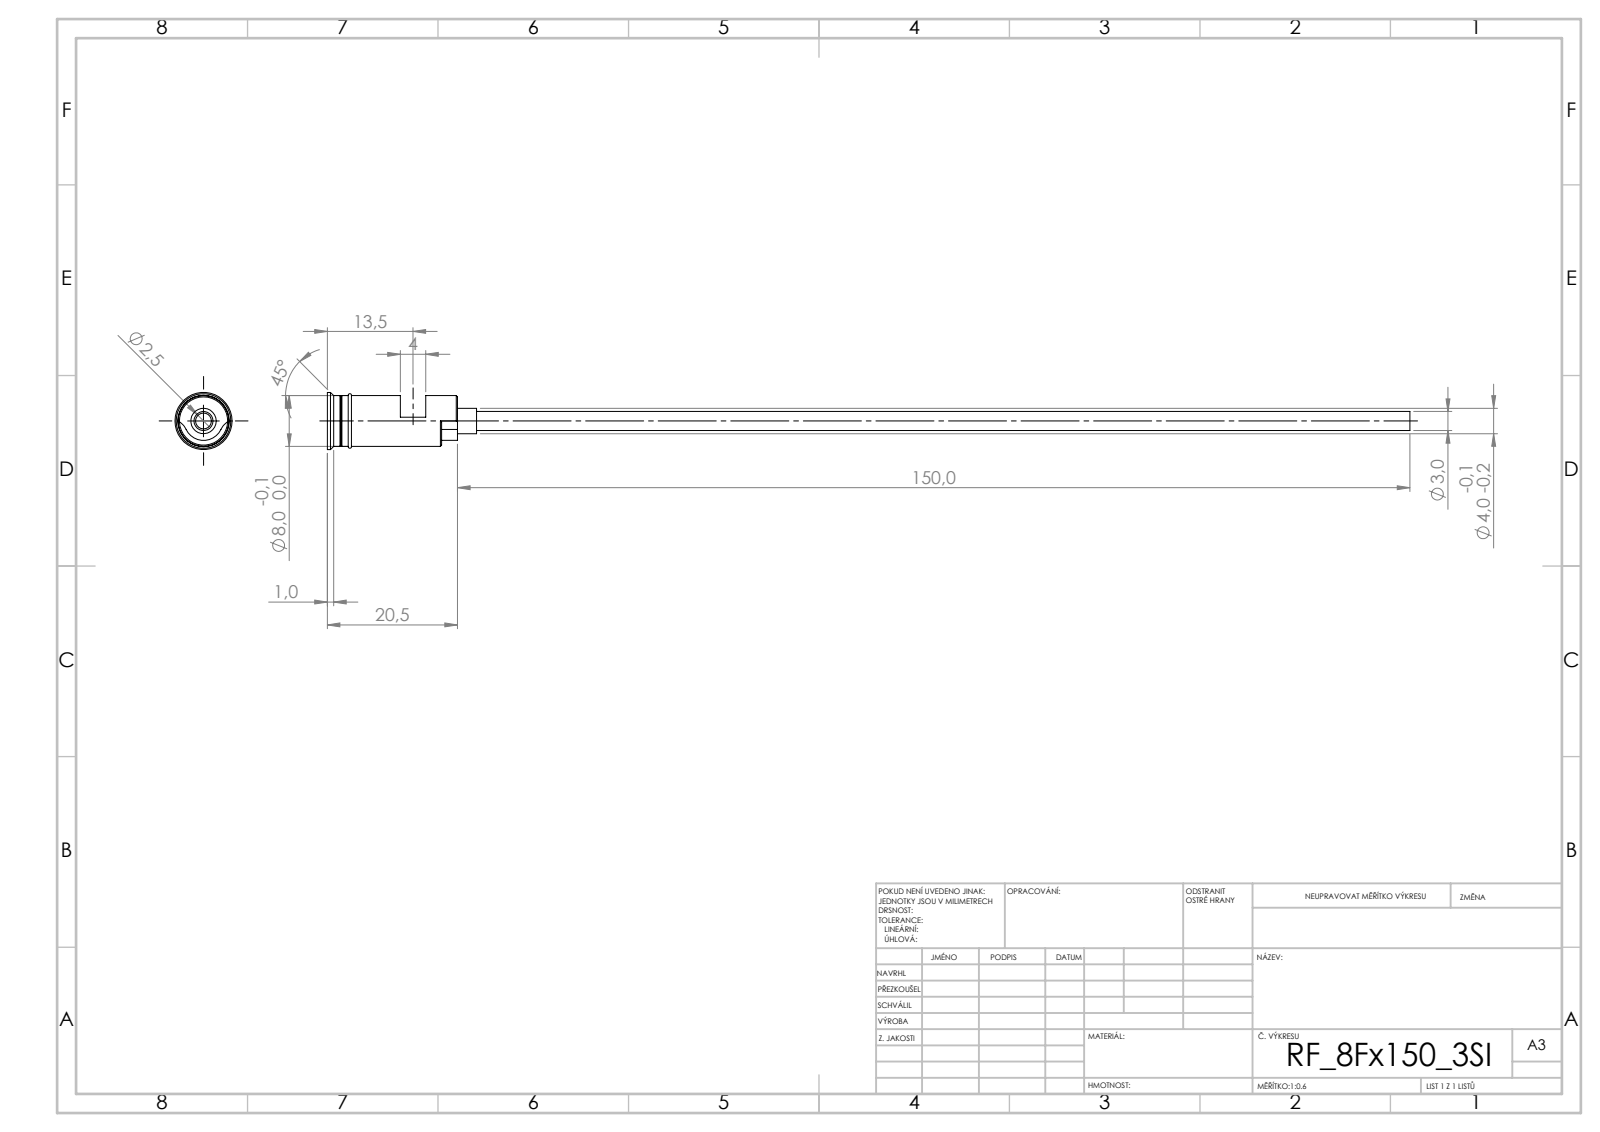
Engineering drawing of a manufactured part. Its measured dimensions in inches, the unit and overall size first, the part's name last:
Units: inches
Overall size (bounding box): 6.713 × 0.354 × 0.354
Round holes (diameter × count): ⌀0.098 ×1
Round bosses / shafts (diameter × count): ⌀0.354 ×1, ⌀0.315 ×1, ⌀0.307 ×1, ⌀0.157 ×1, ⌀0.118 ×1
Partial cylindrical surfaces — rounded edges, fillets, slot ends (radius × count): R0.118 ×2, R0.12 ×1
Main face-to-face distances: 0.157, 0.807, 0.354, 0.453, 0.197, 0.61, 0.098, 0.728, 0.531, 0.374
Volume: 0.074 in³ · Surface area: 5.188 in²
Bodies: 1 solid, 55 faces (24 planar, 19 cylindrical, 12 other)
STEP written by: SolidWorks 2019 (CONFIG_CONTROL_DESIGN)
